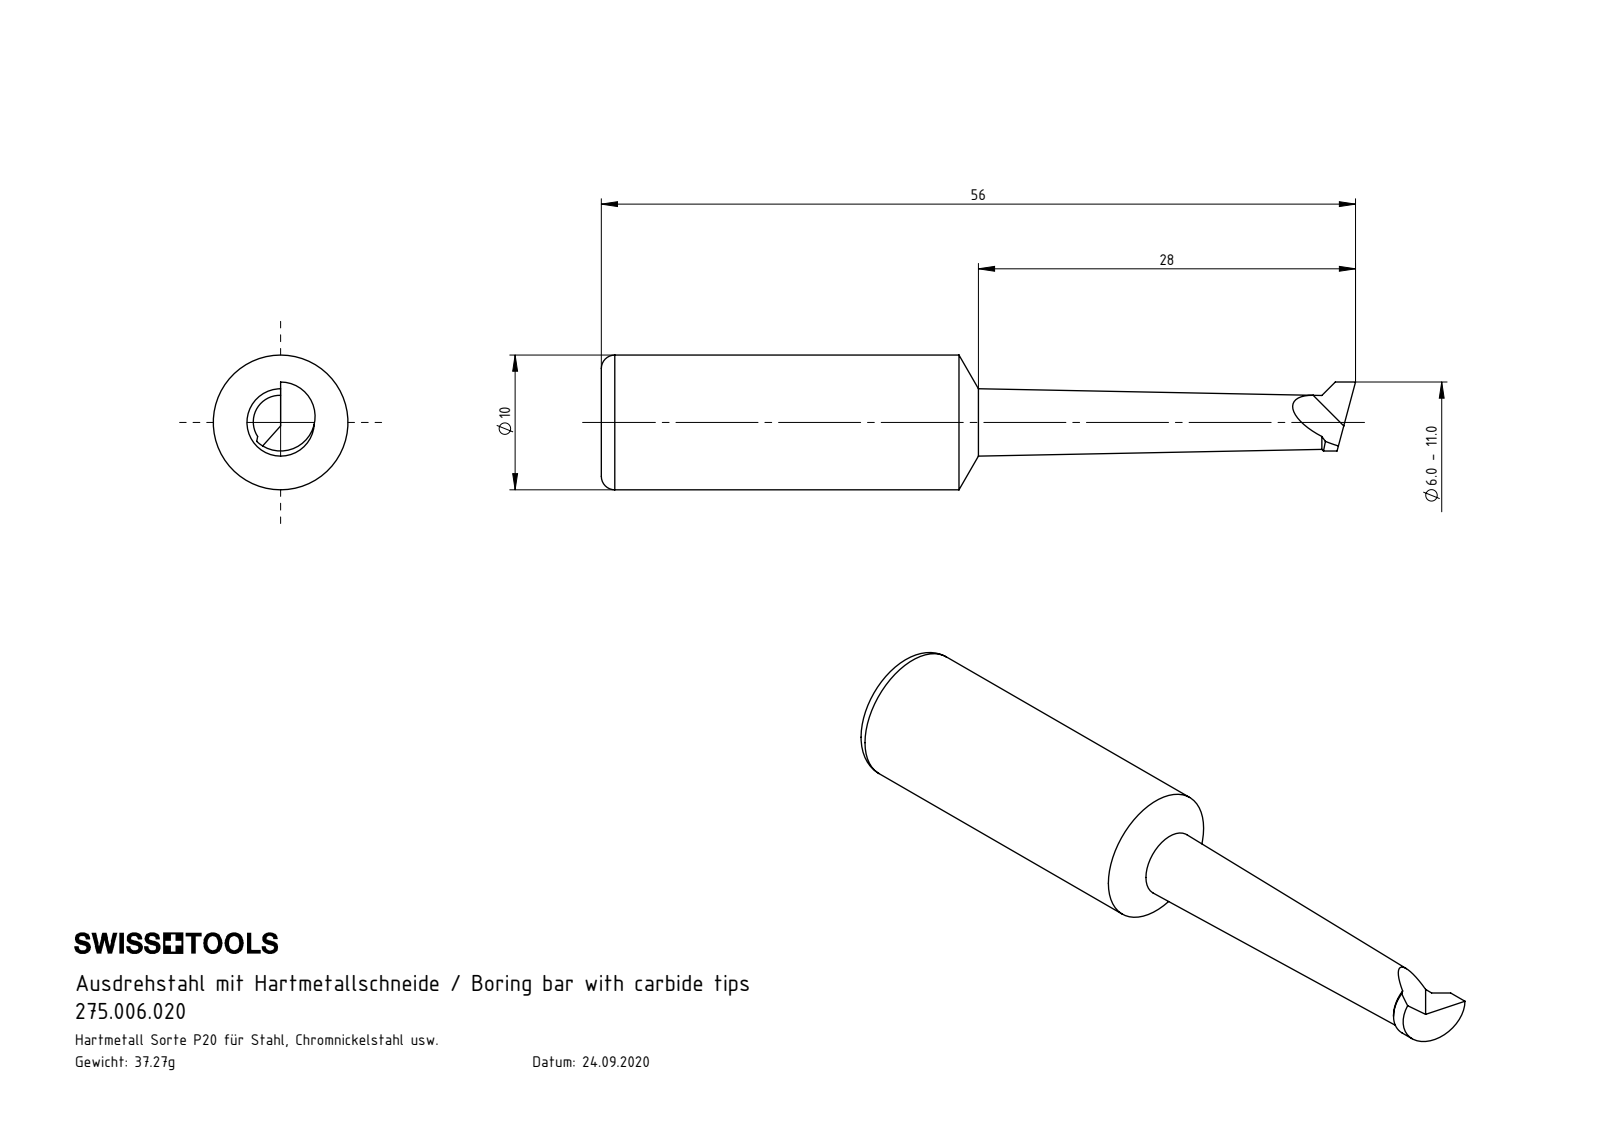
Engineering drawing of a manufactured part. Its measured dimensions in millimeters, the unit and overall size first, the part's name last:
Units: millimetres
Overall size (bounding box): 56 × 10 × 10
Round bosses / shafts (diameter × count): ⌀10 ×1
Partial cylindrical surfaces — rounded edges, fillets, slot ends (radius × count): R2.56 ×1
Volume: 2 570 mm³ · Surface area: 1 367 mm²
Bodies: 1 solid, 14 faces (4 planar, 3 cylindrical, 7 other)
Part name (STEP PRODUCT): 275.006.020
STEP written by: SolidWorks 2022 (AUTOMOTIVE_DESIGN)
